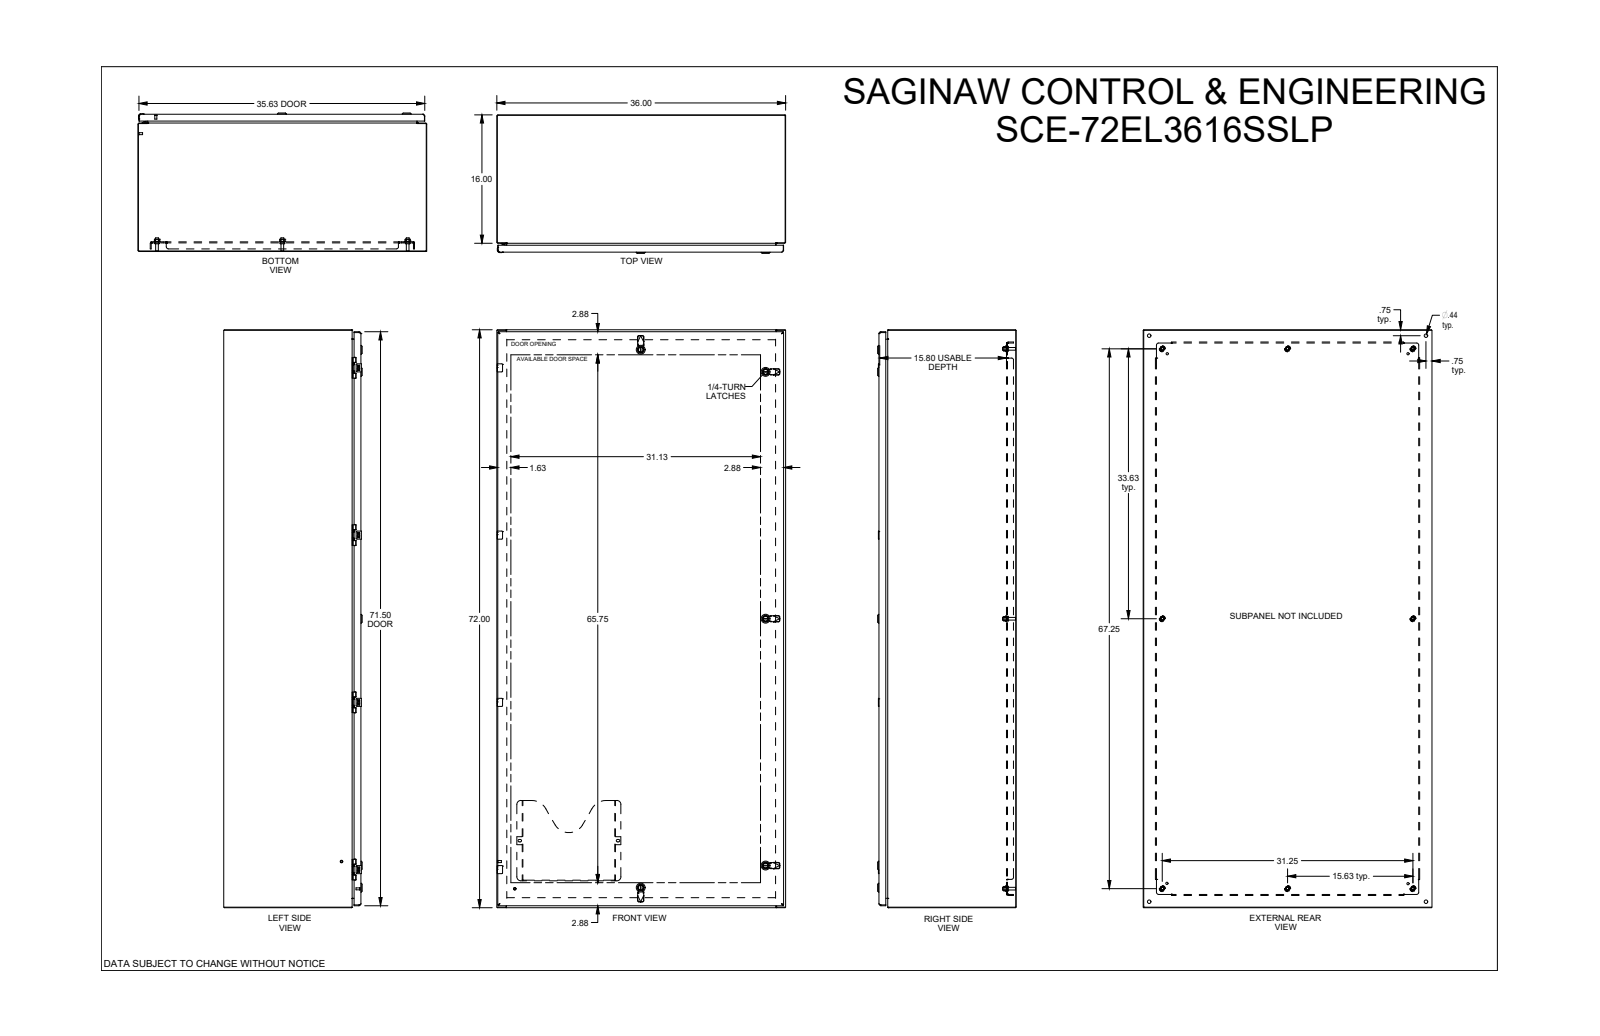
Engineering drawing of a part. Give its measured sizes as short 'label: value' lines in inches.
name: SCE-72EL3616SSLP
written by: SolidWorks 2019 (CONFIG_CONTROL_DESIGN)
unit: in
bodies: 0 solids, 5420 faces (2661 planar, 1535 cylindrical, 1224 other)
size: 72 × 36 × 17.256
holes: 15× ⌀0.394, 8× ⌀0.172, 8× ⌀0.205, 8× ⌀0.244, 8× ⌀0.266, 8× ⌀0.367, 8× ⌀0.375, 8× ⌀0.5, 5× ⌀0.197, 5× ⌀0.315, 5× ⌀0.634, 4× ⌀0.156
bosses: 12× ⌀0.17, 8× ⌀0.366, 8× ⌀0.332, 8× ⌀0.25, 5× ⌀1.102, 5× ⌀0.866, 5× ⌀0.802, 5× ⌀0.78
rounds: 142× R0.012, 52× R0.01, 52× R0.02, 48× R0.015, 23× R0.04, 20× R0.157, 17× R0.03, 16× R0.031
face distances: 0.075, 0.104, 16.995, 16.92, 1, 17.099, 17.024, 0.075, 1.125, 15.795
hole spacings: 2.461, 20.833, 41.667, 1.274, 4.754, 3.48, 4.262, 20.833
